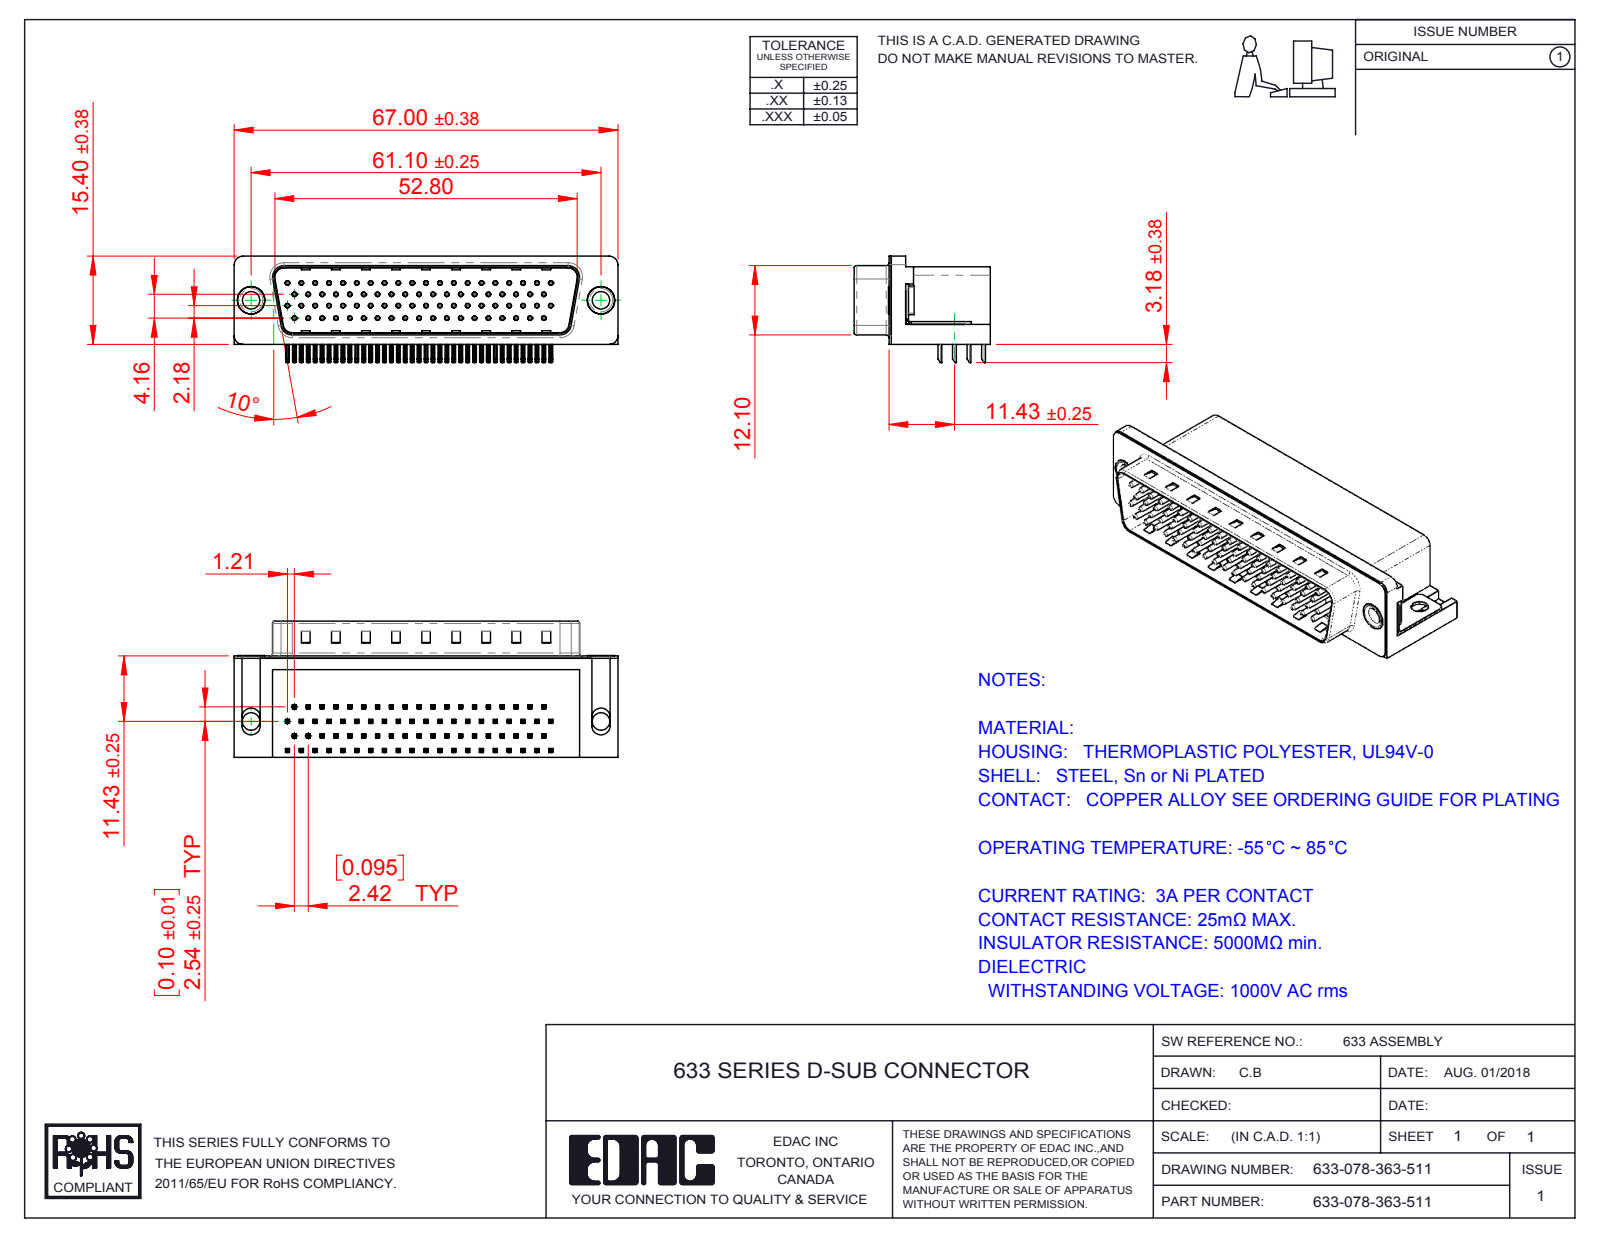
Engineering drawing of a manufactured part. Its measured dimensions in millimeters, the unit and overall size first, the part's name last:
Units: millimetres
Overall size (bounding box): 67 × 23.8 × 18.58
Round holes (diameter × count): ⌀0.35 ×78, ⌀0.8 ×78, ⌀3.05 ×4, ⌀4 ×2, ⌀4.8 ×2, ⌀5 ×2
Round bosses / shafts (diameter × count): ⌀0.75 ×78, ⌀4.9 ×2, ⌀4.75 ×2, ⌀3.85 ×2
Partial cylindrical surfaces — rounded edges, fillets, slot ends (radius × count): R0.25 ×320, R0.12 ×156, R1 ×16, R0.5 ×9, R1.6 ×8, R1.5 ×6, R0.45 ×4, R0.9 ×4
Main face-to-face distances: 0.4, 13.2, 17.3, 11.7, 13.35, 2.05, 13.75, 1.65, 1.85, 11.9
Hole centre spacings: 2.42, 4.84, 7.26, 9.68, 6.26, 7.13, 12.1, 8.62
Volume: 14 599 mm³ · Surface area: 16 316 mm²
Bodies: 84 solids, 6234 faces (3979 planar, 1760 cylindrical, 495 other)
Part name (STEP PRODUCT): 633 Contact Top 78; 633 Thru Hole Board Mount_78 Contact; 633 Contact Top_78 Contact; 633 Contact Middle_78 Contact (+5 more)
STEP written by: SolidWorks 2016 (CONFIG_CONTROL_DESIGN)
